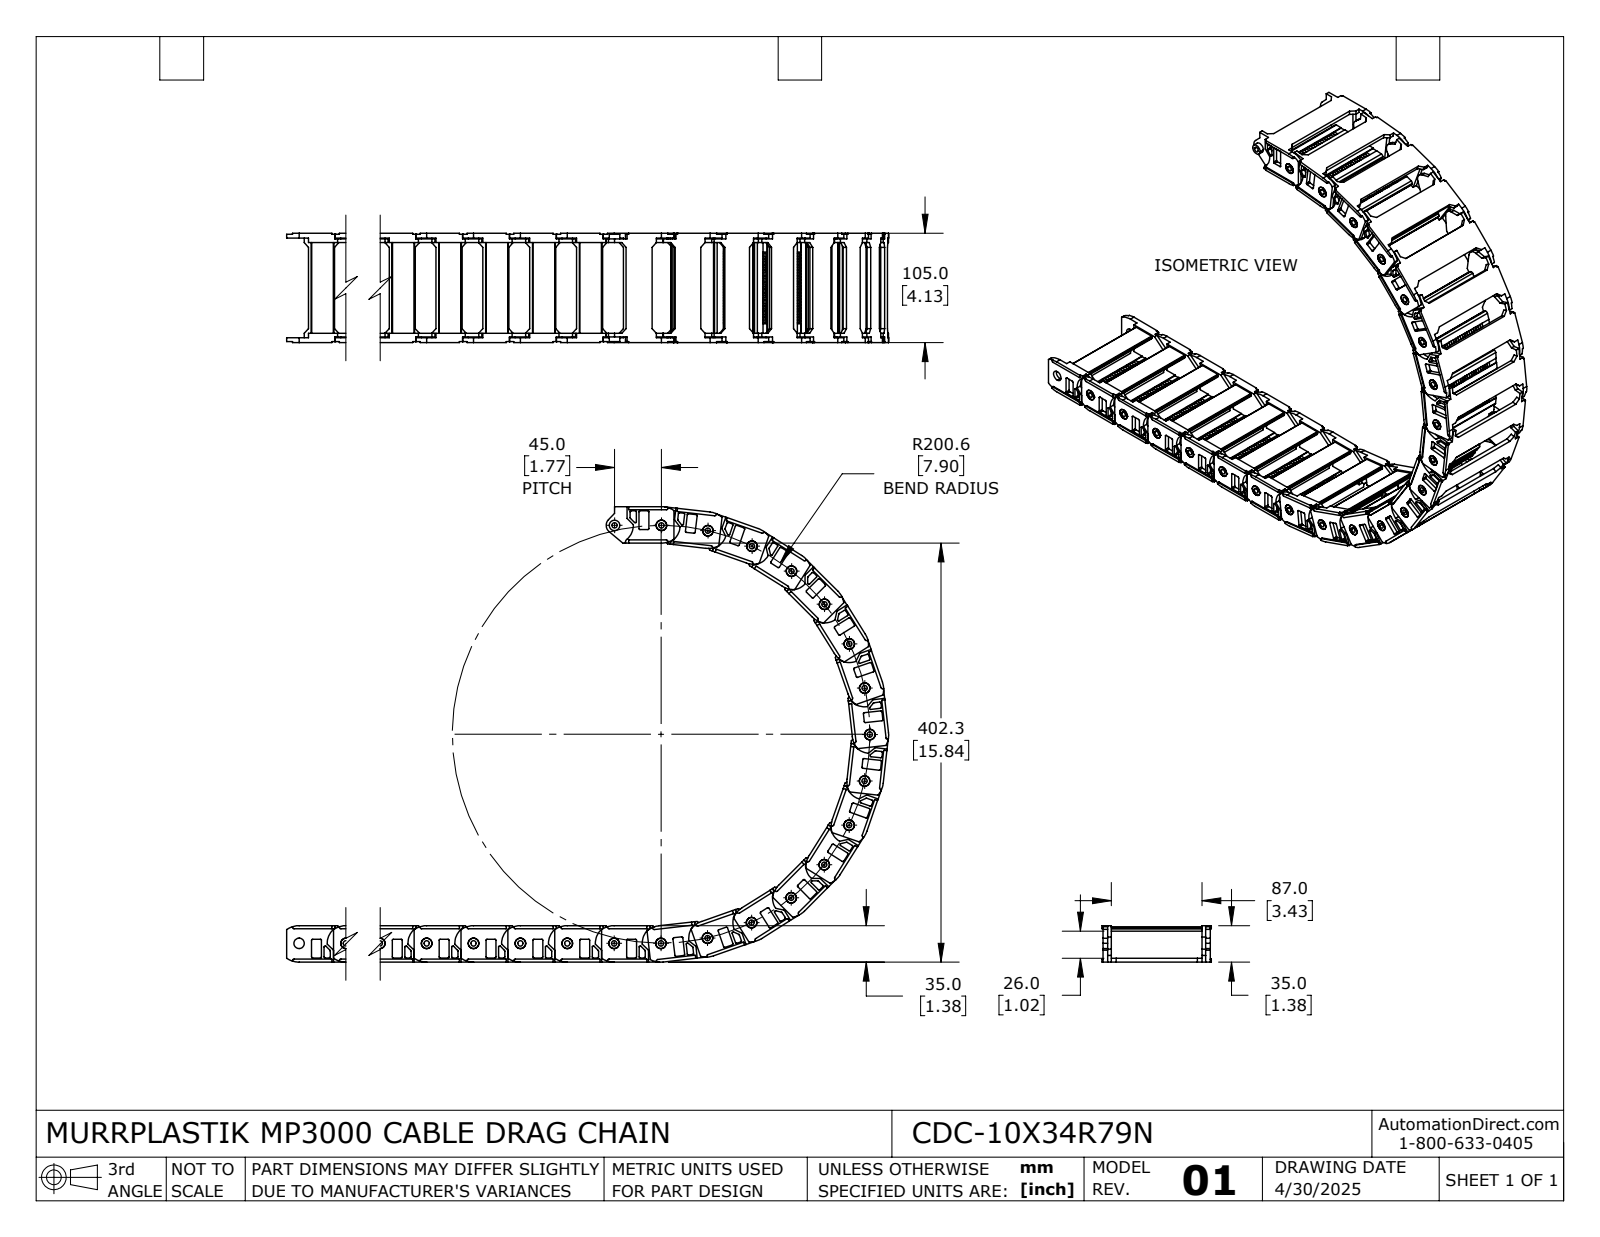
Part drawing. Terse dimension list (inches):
name: CDC-10X34R79N
written by: SolidWorks 2024 (AUTOMOTIVE_DESIGN)
unit: in
bodies: 22 solids, 5104 faces (4004 planar, 1100 cylindrical, 0 other)
size: 21.483 × 17.216 × 4.134
volume: 47.13 in³; area: 739 in²
holes: 22× ⌀0.201, 22× ⌀0.398
bosses: 22× ⌀0.394
rounds: 176× R0.039, 88× R0.02, 44× R0.059, 44× R0.079, 44× R0.827, 22× R0.11, 22× R0.315, 22× R0.709
face distances: 3.74, 0.315, 0.157, 0.146, 3.909, 0.169, 3.594, 0.138, 3.425, 1.181
hole spacings: 1.772, 1.767, 1.763, 3.513, 6.85, 3.508, 3.512, 3.517
